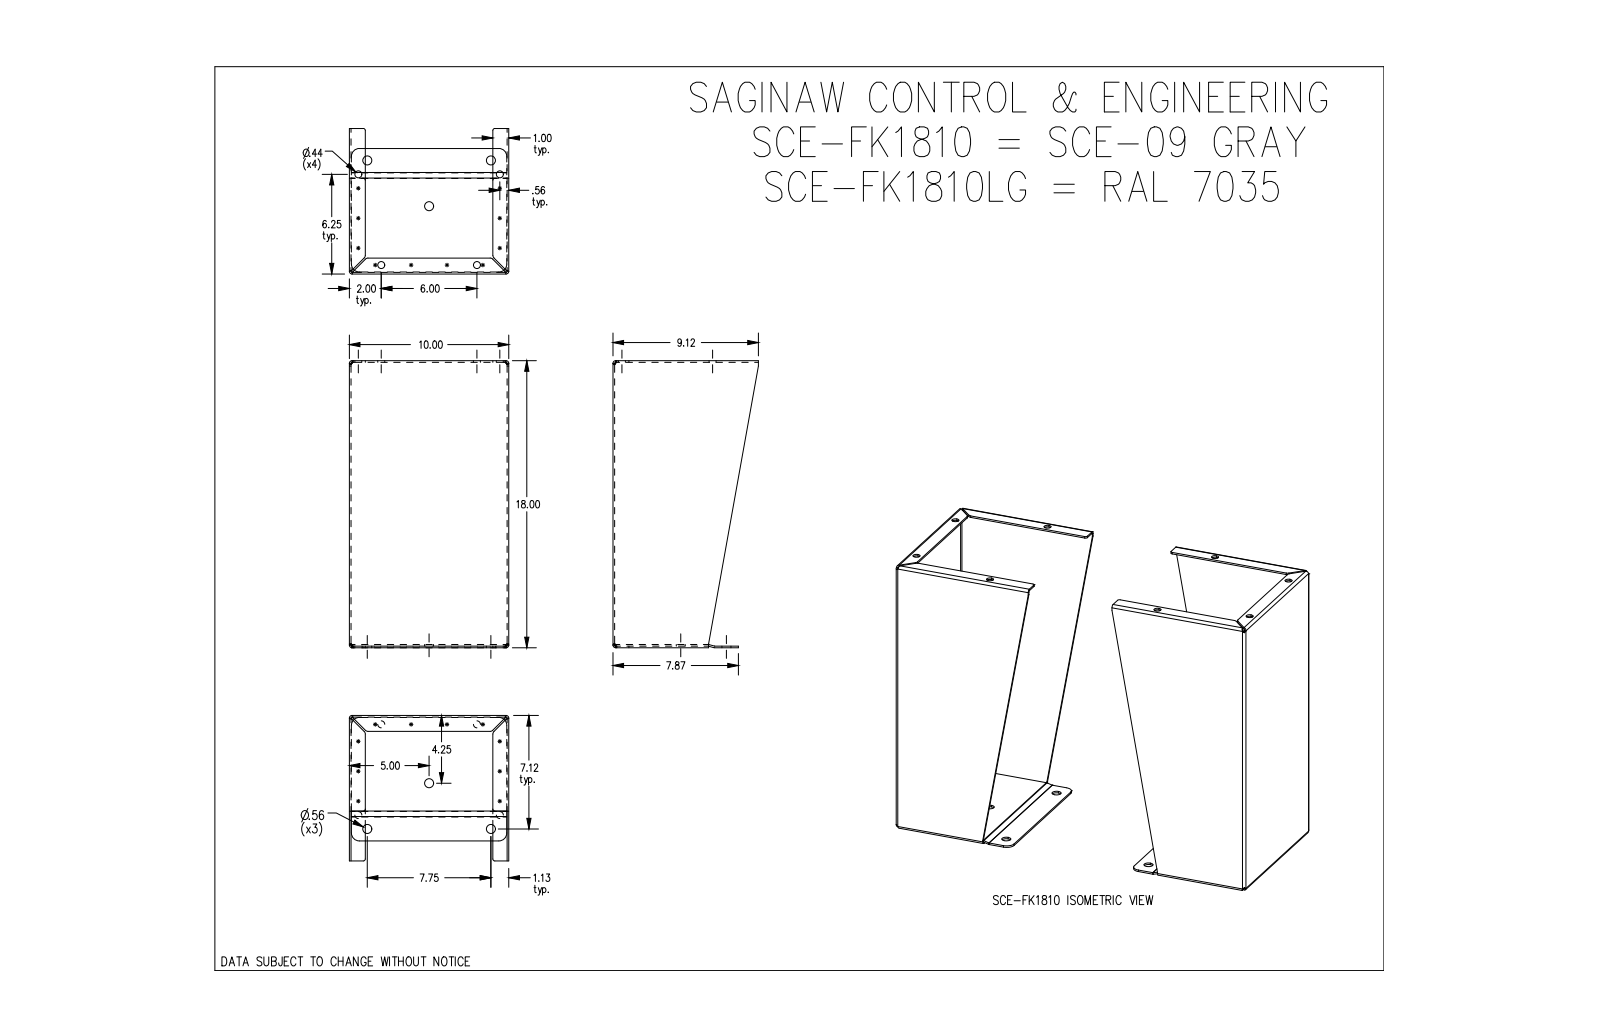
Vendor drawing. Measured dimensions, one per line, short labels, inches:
name: SCE-FK1810
written by: SolidWorks 2019 (CONFIG_CONTROL_DESIGN)
unit: in
bodies: 4 solids, 214 faces (96 planar, 86 cylindrical, 32 other)
size: 24 × 18 × 10
volume: 116.3 in³; area: 2 265 in²
holes: 8× ⌀0.437, 6× ⌀0.563
rounds: 16× R0.166, 12× R0.063, 8× R0.125, 8× R0.22, 8× R0.5, 6× R0.062
face distances: 0.104, 9.896, 23.896, 9.792, 10, 24, 23.792, 17.792, 17.896, 0.101
hole spacings: 1.035, 4.755, 4.867, 5.866, 6.614, 9.363, 10.646, 13.211
